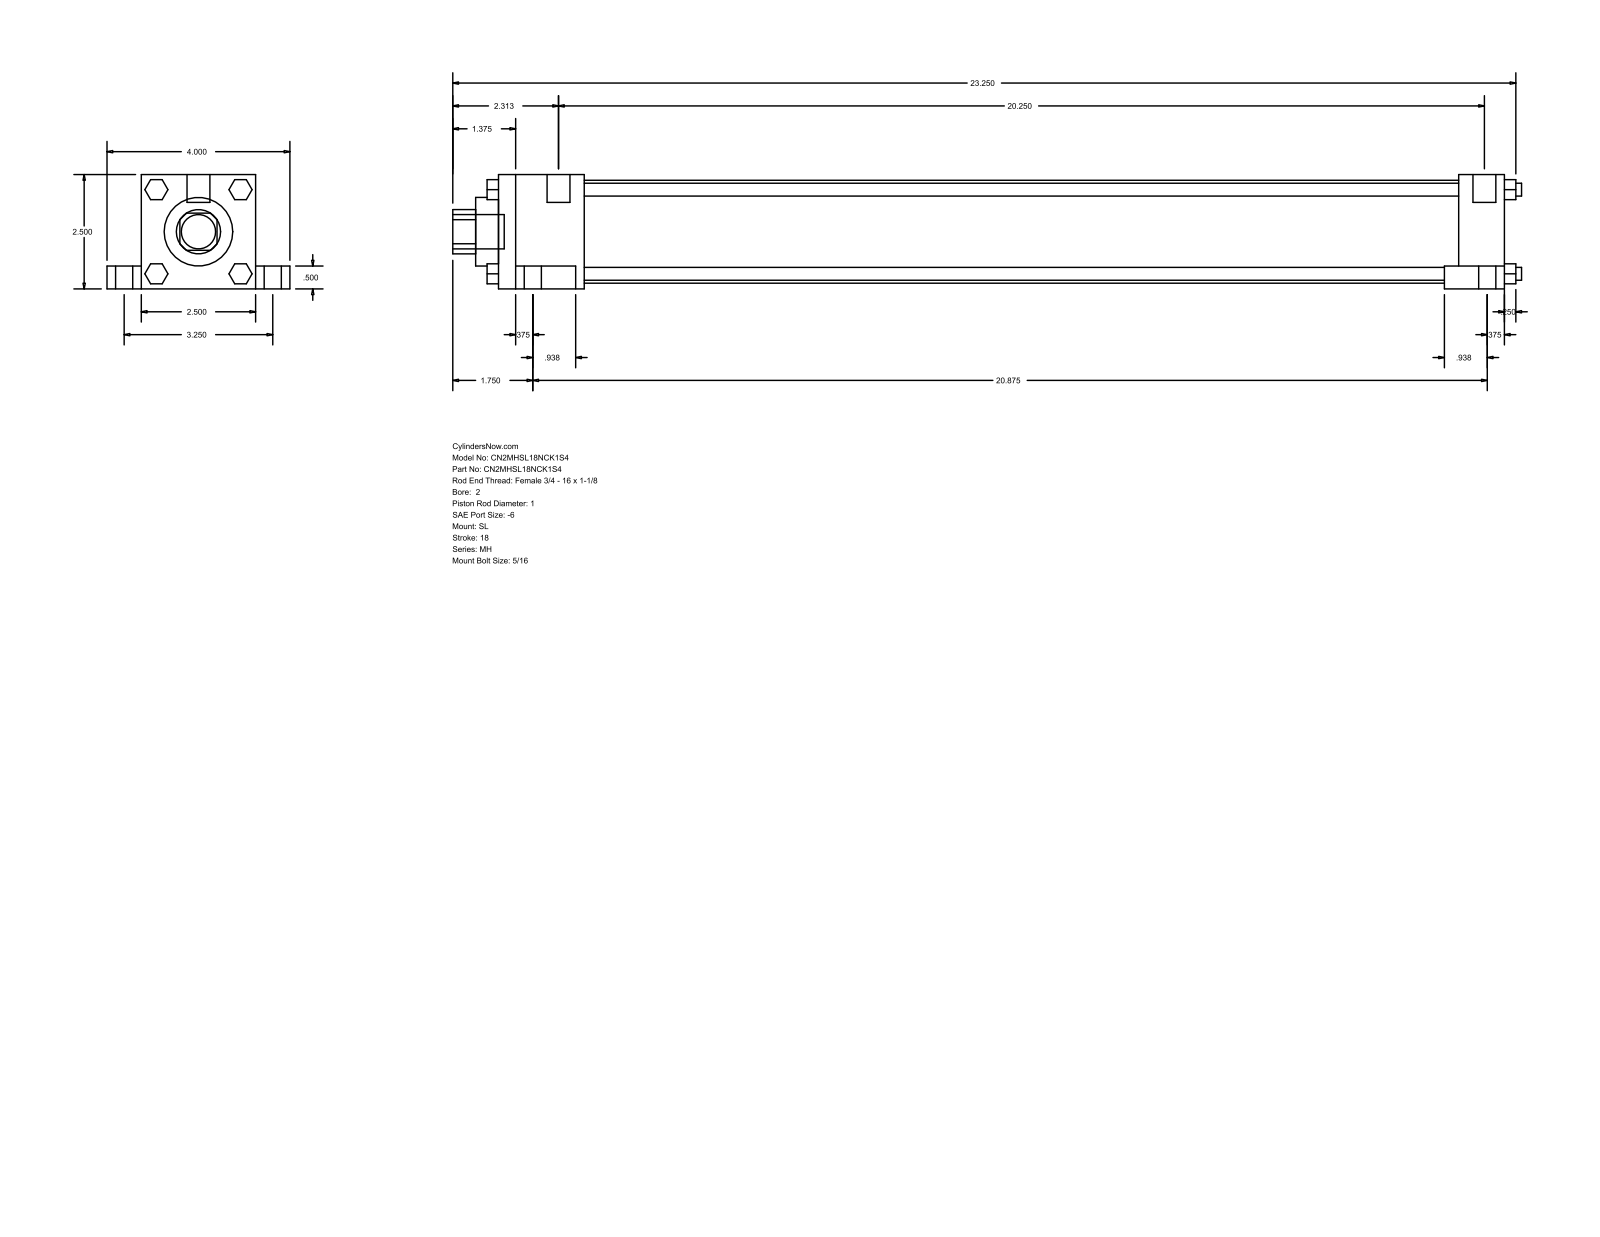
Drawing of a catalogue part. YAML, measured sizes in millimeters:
part_name: "MH_SL__0200_1"
step_written_by: "GSSL Pune (CONFIG_CONTROL_DESIGN)"
units: millimeters
bodies: {solids: 0, faces: 148, planar: 112, cylindrical: 36, other: 0}
overall_size: [593.73, 101.6, 63.5]
round_holes:
  - {diameter: 25.4, count: 1}
  - {diameter: 38.1, count: 1}
  - {diameter: 57.15, count: 1}
round_bosses_or_shafts:
  - {diameter: 15.88, count: 4}
  - {diameter: 9.53, count: 4}
  - {diameter: 7.14, count: 4}
  - {diameter: 5.56, count: 4}
  - {diameter: 12.7, count: 2}
  - {diameter: 19.05, count: 1}
partial_cylinders:
  - {radius: 12.29, count: 1}
face_to_face_distances: [63.5, 558.8, 12.7, 19.05, 50.8, 82.55, 25.4, 9.52, 533.4, 47.63]
